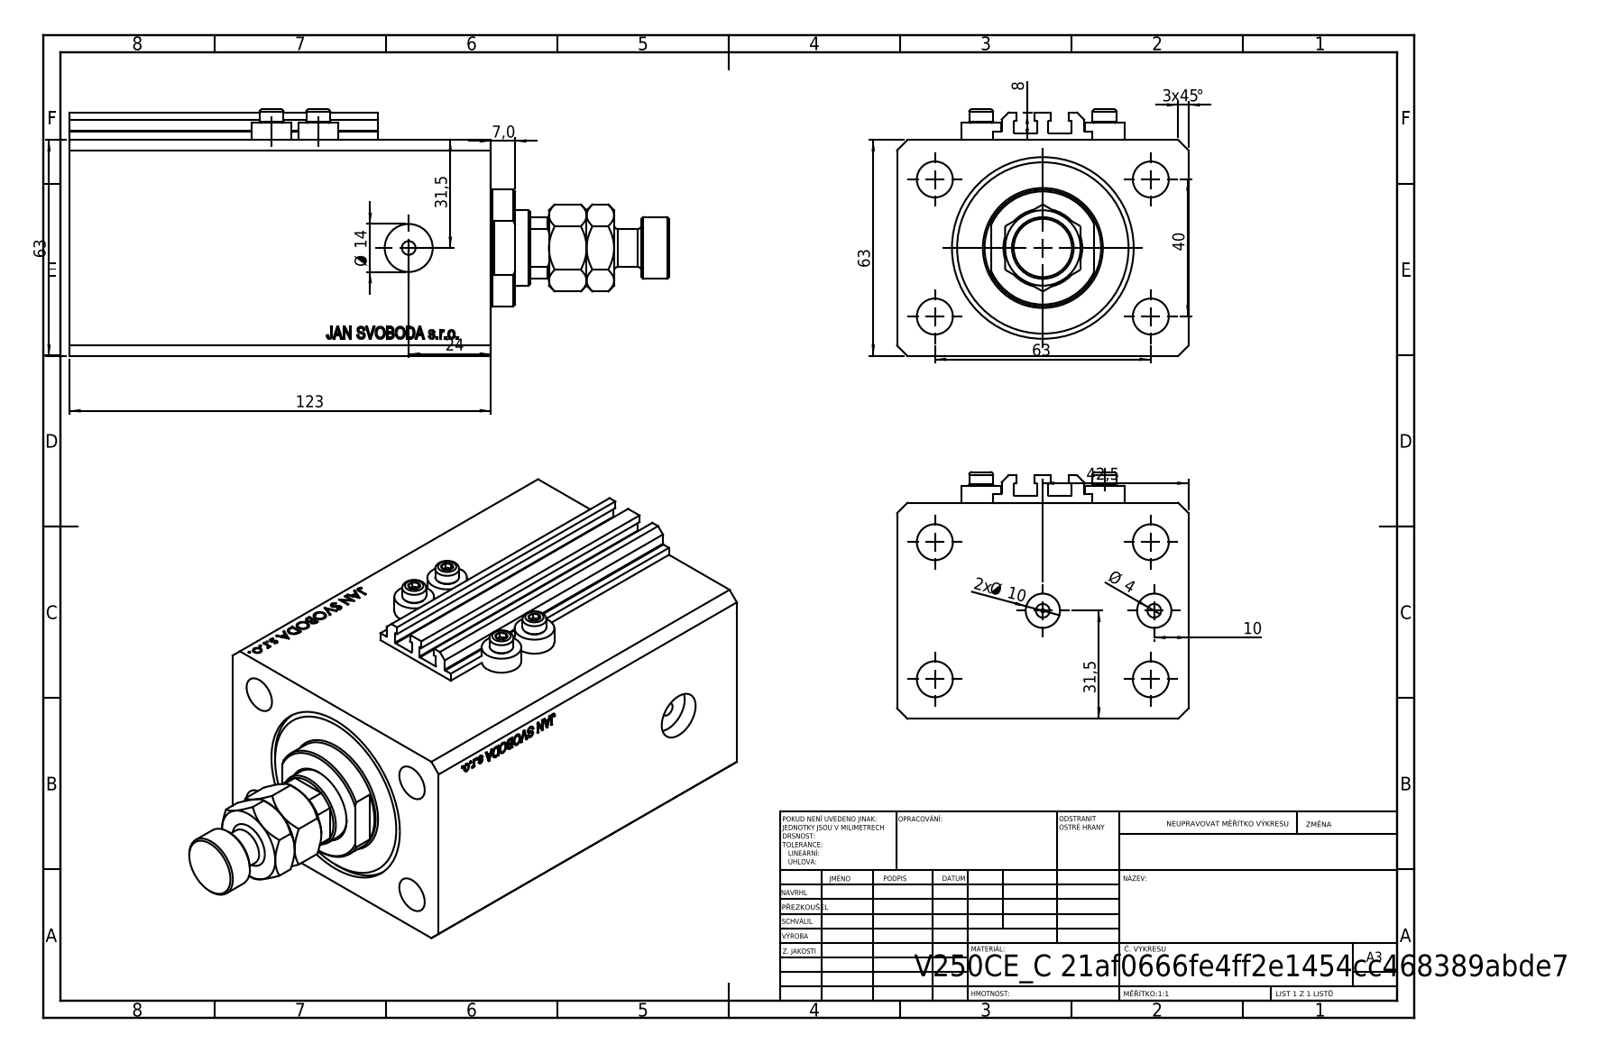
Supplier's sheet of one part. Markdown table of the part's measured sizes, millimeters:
| quantity | value |
| --- | --- |
| part name | V250CE_VC_C; V250CE_C_Body; ALLEN BOLT V250CE; MFA (+1 more) |
| STEP written by | SolidWorks 2019 (CONFIG_CONTROL_DESIGN) |
| units | millimeters |
| bodies | 9 solids, 1090 faces (520 planar, 92 cylindrical, 478 other) |
| overall size | 174.9 × 85 × 72 |
| volume | 597 590 mm³ |
| surface area | 119 547 mm² |
| round holes (diameter × count) | 4 × 8, 10.5 × 4, 10 × 2, 14 × 2, 1.25 × 1, 12.5 × 1, 22 × 1, 40 × 1, 53 × 1 |
| round bosses / shafts (diameter × count) | 11.6 × 4, 7 × 4, 34 × 1, 18 × 1, 11 × 1 |
| partial cylindrical surfaces (radius × count) | 0.2 × 10, 10.5 × 1 |
| main face-to-face distances | 63, 85, 123, 95.9, 27.1, 11.4, 84.5, 111.6, 2.5, 2 |
| hole center spacings | 37.31, 13.6, 20.02, 36, 38.48, 40, 63, 67.05 |
